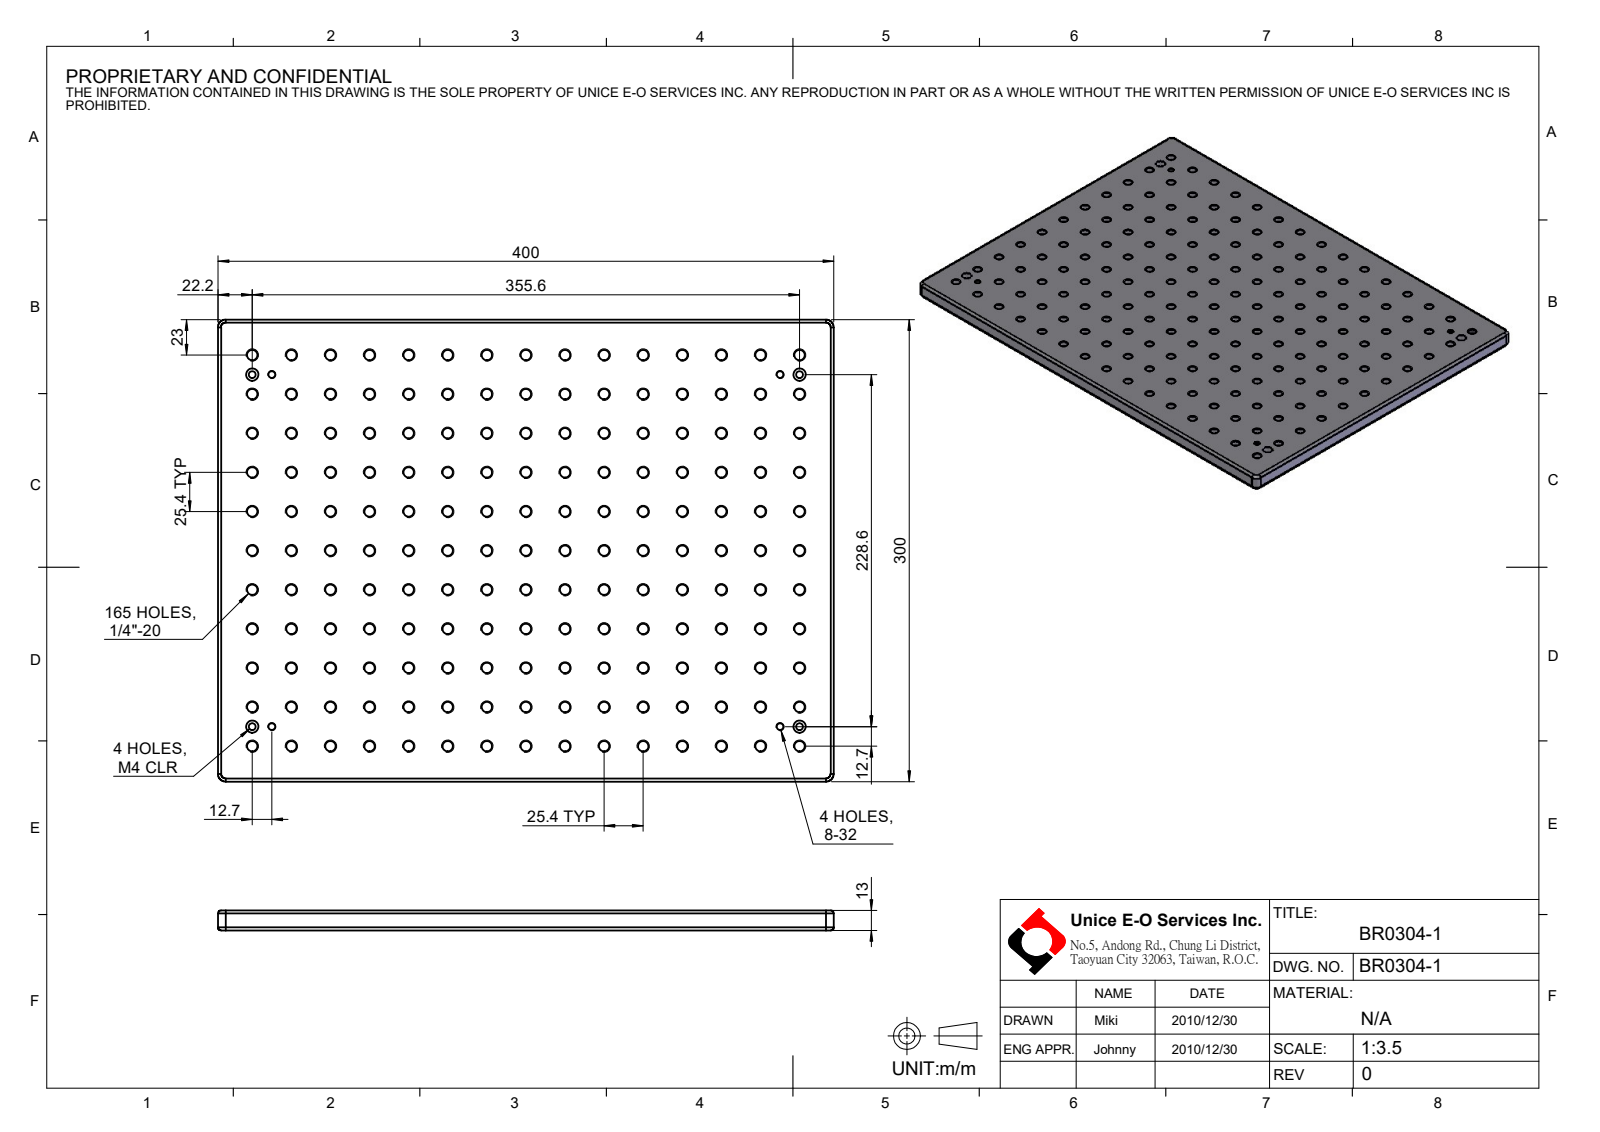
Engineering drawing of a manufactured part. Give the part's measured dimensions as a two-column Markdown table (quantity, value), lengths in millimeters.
| quantity | value |
| --- | --- |
| part name | BR0304-1 |
| STEP written by | SolidWorks 2016 (CONFIG_CONTROL_DESIGN) |
| units | millimeters |
| bodies | 1 solid, 384 faces (10 planar, 366 cylindrical, 8 other) |
| overall size | 400 × 300 × 13 |
| volume | 1 478 000 mm³ |
| surface area | 290 820 mm² |
| round holes (diameter × count) | 6.76 × 165, 4.39 × 4, 4.5 × 4, 8 × 4 |
| partial cylindrical surfaces (radius × count) | 2 × 8, 5 × 4 |
| main face-to-face distances | 13, 300, 400, 7, 6 |
| hole center spacings | 25.4, 50.8, 76.2, 127, 101.6, 255.27, 259.03, 12.7 |
